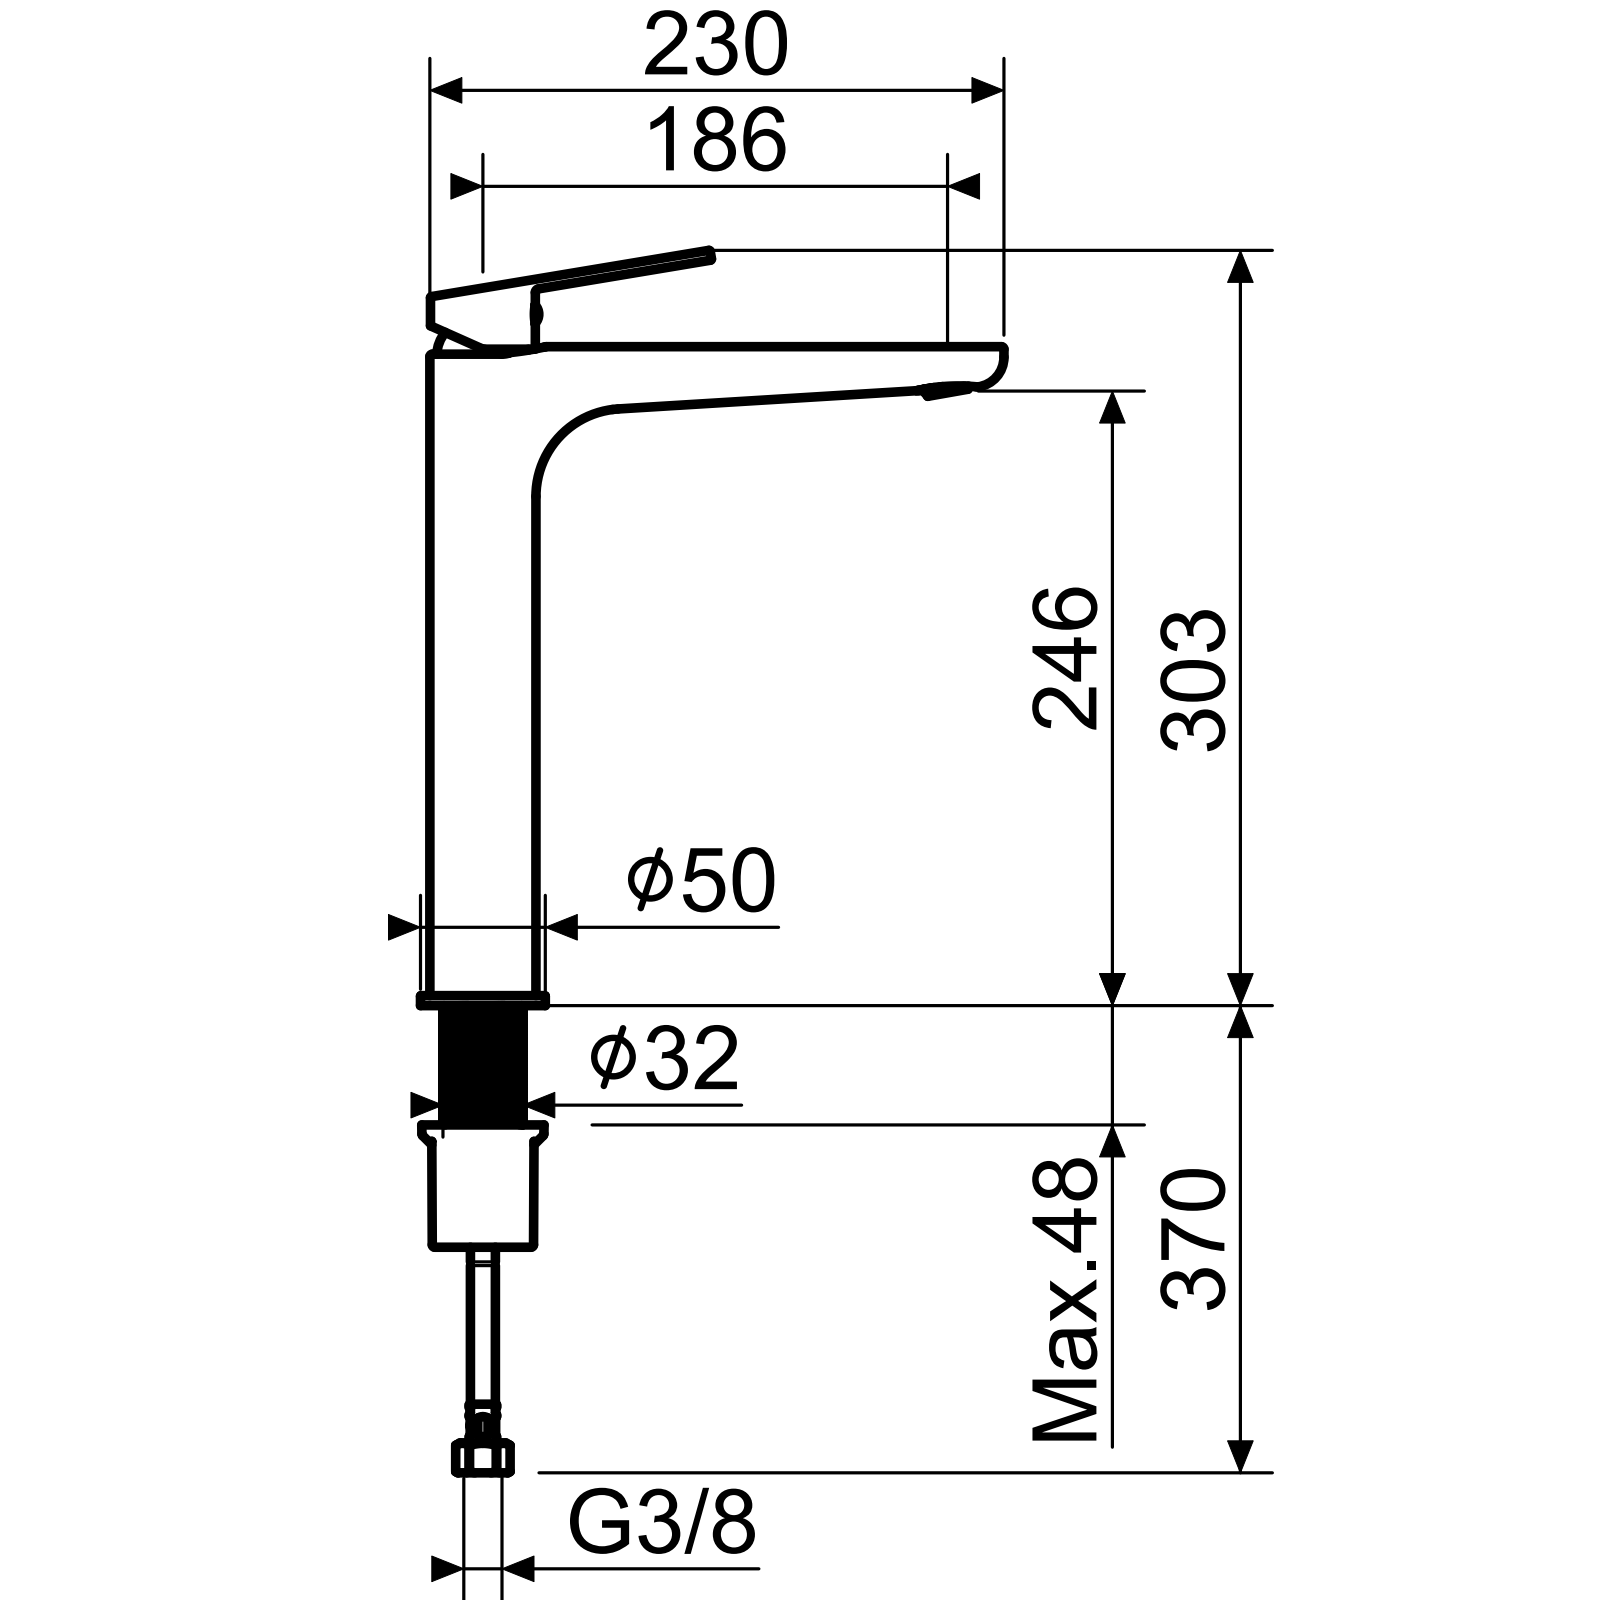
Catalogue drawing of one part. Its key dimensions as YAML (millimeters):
part_name: "TAO0052_-_CON_AERATORE"
step_written_by: "CREO PARAMETRIC BY PTC INC, 2020281 (CONFIG_CONTROL_DESIGN)"
units: millimeters
bodies: {solids: 1, faces: 104, planar: 18, cylindrical: 36, other: 50}
overall_size: [300.98, 234, 50]
volume: 563684
surface_area: 69347
round_bosses_or_shafts:
  - {diameter: 50, count: 1}
  - {diameter: 42, count: 1}
  - {diameter: 24, count: 1}
partial_cylinders:
  - {radius: 0.5, count: 11}
  - {radius: 5, count: 2}
  - {radius: 15, count: 2}
  - {radius: 55.48, count: 2}
  - {radius: 55.66, count: 2}
  - {radius: 145.89, count: 2}
  - {radius: 149.66, count: 2}
  - {radius: 0.4, count: 1}
face_to_face_distances: [42, 5, 2, 264, 259, 262, 257, 266, 261, 4]
